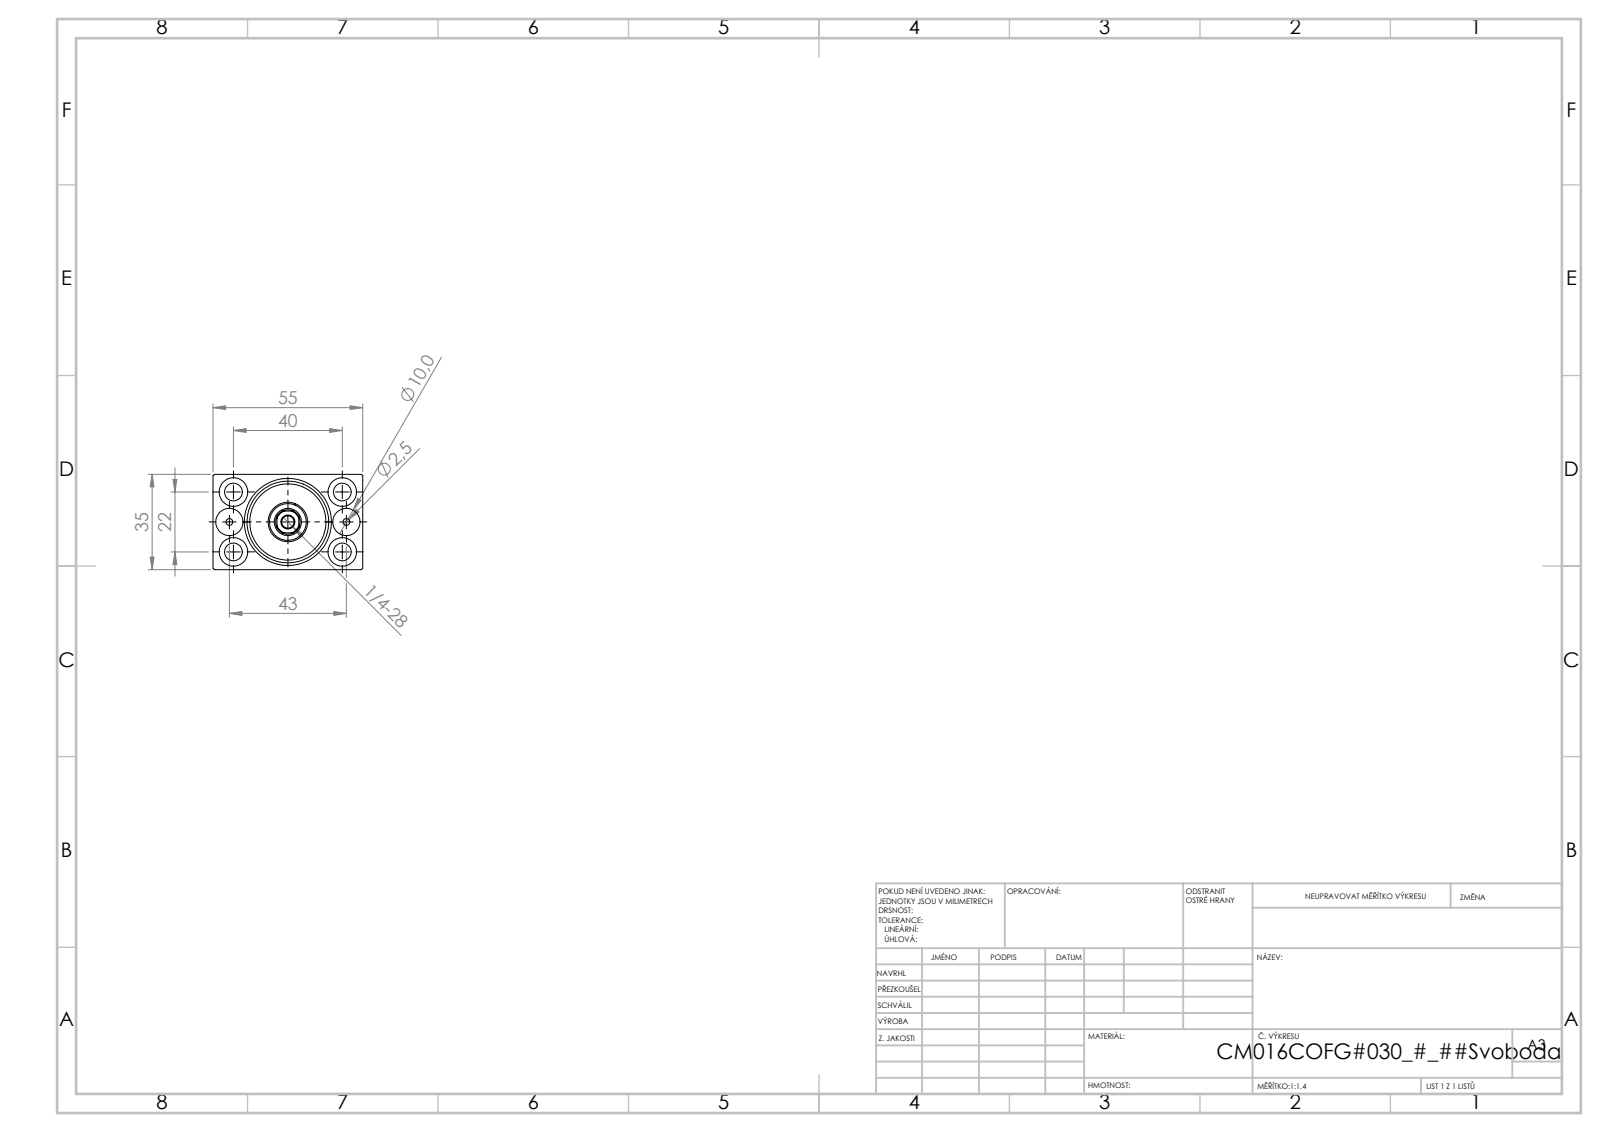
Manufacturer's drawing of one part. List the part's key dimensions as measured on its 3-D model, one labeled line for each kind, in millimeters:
Part name (STEP PRODUCT): V450CM_C_Body; V450CM_C_VCP; V450CM_VC_B
STEP written by: SolidWorks 2019 (CONFIG_CONTROL_DESIGN)
Units: millimetres
Bodies: 3 solids, 861 faces (409 planar, 58 cylindrical, 394 other)
Overall size (bounding box): 85 × 55 × 35
Volume: 129 437 mm³ · Surface area: 35 806 mm²
Round holes (diameter × count): ⌀6.5 ×4, ⌀10.5 ×4, ⌀10 ×3, ⌀2.5 ×2, ⌀4.5 ×1, ⌀13.5 ×1, ⌀14.5 ×1, ⌀16 ×1, ⌀18 ×1, ⌀30 ×1
Partial cylindrical surfaces — rounded edges, fillets, slot ends (radius × count): R4.5 ×1
Main face-to-face distances: 35, 55, 71, 5, 2, 76, 3, 66, 8, 79
Hole centre spacings: 11.1, 22.83, 42.93, 21.5, 22, 40, 45.65, 43
